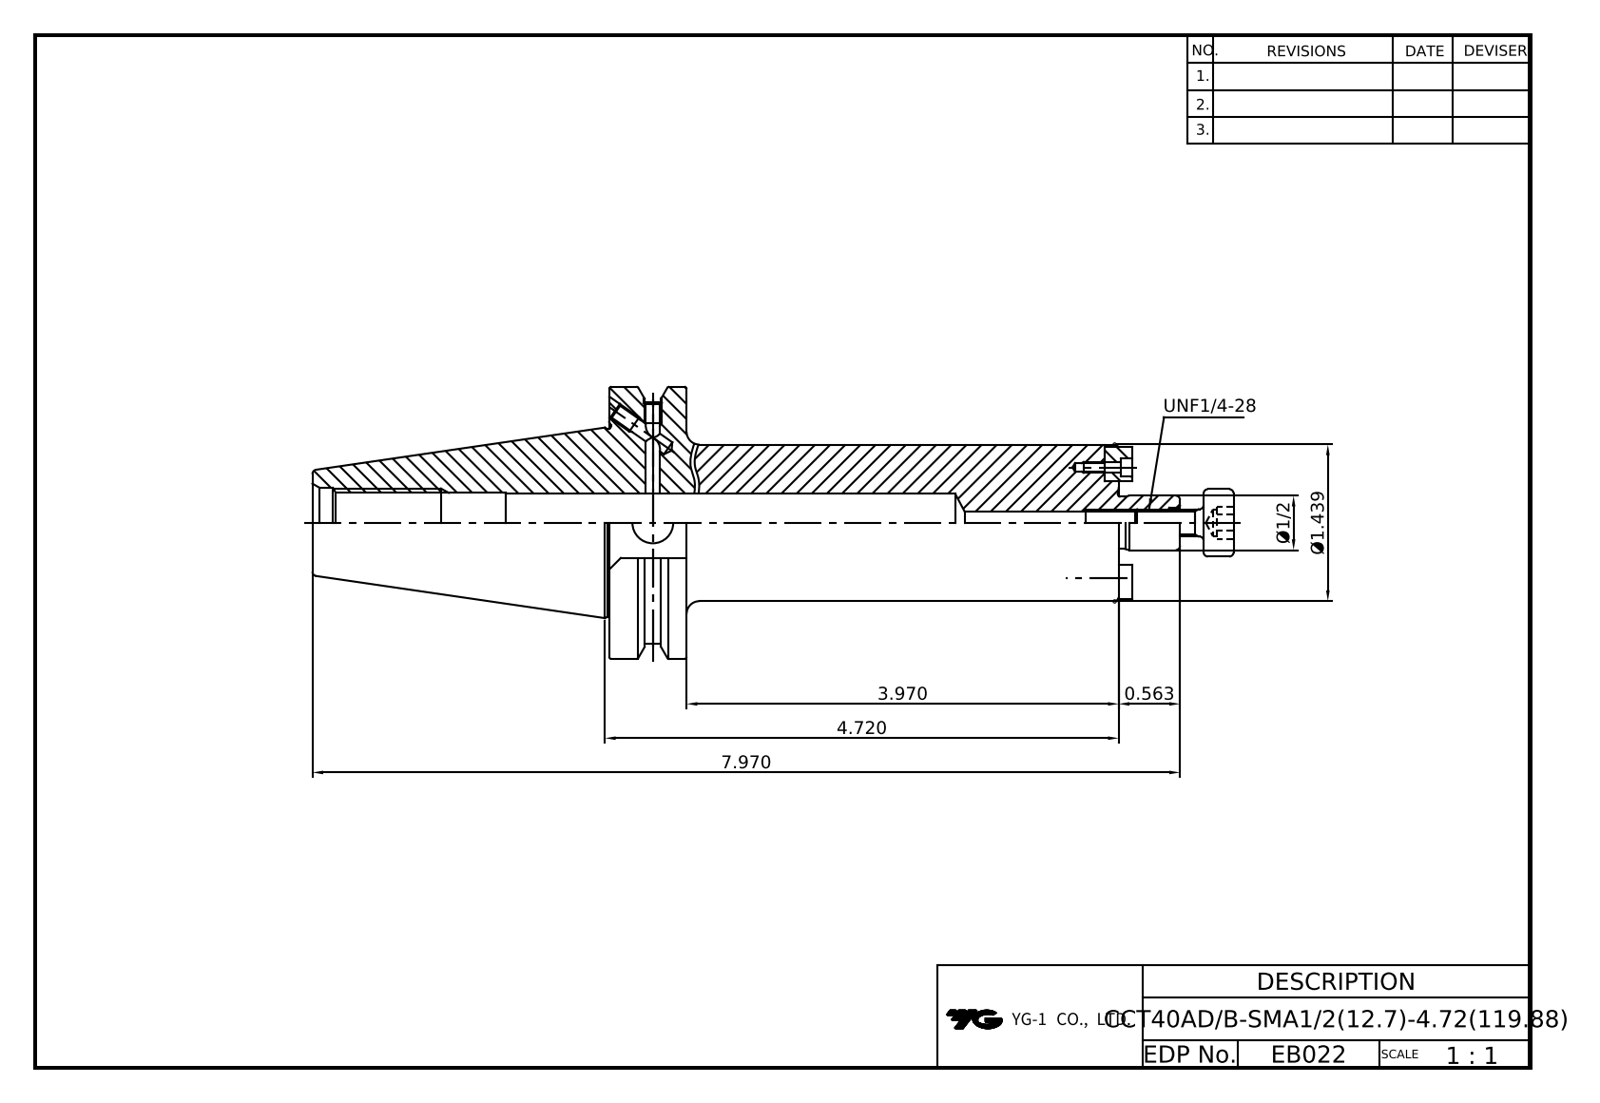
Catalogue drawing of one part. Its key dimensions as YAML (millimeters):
part_name: "CCT40ADB-SMA12.7-119.888; DRIVE KEY-6.35x6.35x8; HEX'' WRENCH BOLT-UNC#3-48x1_4L; COLLAR BOLT-UNF1_4-28x16L"
step_written_by: "Autodesk Inventor 2020 (AUTOMOTIVE_DESIGN)"
units: millimeters
bodies: {solids: 6, faces: 179, planar: 90, cylindrical: 47, other: 42}
overall_size: [214.4, 63.5, 61.1]
volume: 203700
surface_area: 38610
round_holes:
  - {diameter: 3.3, count: 4}
  - {diameter: 4.2, count: 4}
  - {diameter: 1.9, count: 2}
  - {diameter: 2.6, count: 2}
  - {diameter: 4, count: 2}
  - {diameter: 5.4, count: 1}
  - {diameter: 6.4, count: 1}
  - {diameter: 7, count: 1}
  - {diameter: 9.5, count: 1}
  - {diameter: 13, count: 1}
  - {diameter: 13.4, count: 1}
  - {diameter: 16.3, count: 1}
round_bosses_or_shafts:
  - {diameter: 4.1, count: 2}
  - {diameter: 2.5, count: 2}
  - {diameter: 63.5, count: 1}
  - {diameter: 43.8, count: 1}
  - {diameter: 36.5, count: 1}
  - {diameter: 15.7, count: 1}
  - {diameter: 12.7, count: 1}
  - {diameter: 12.2, count: 1}
partial_cylinders:
  - {radius: 3.2, count: 2}
  - {radius: 28.1, count: 1}
face_to_face_distances: [18.1, 118.9, 100.8, 47.6, 16.4, 3.2, 115.7, 97.6, 6.4, 69.2]
hole_center_spacings: [12.9, 25.9]
